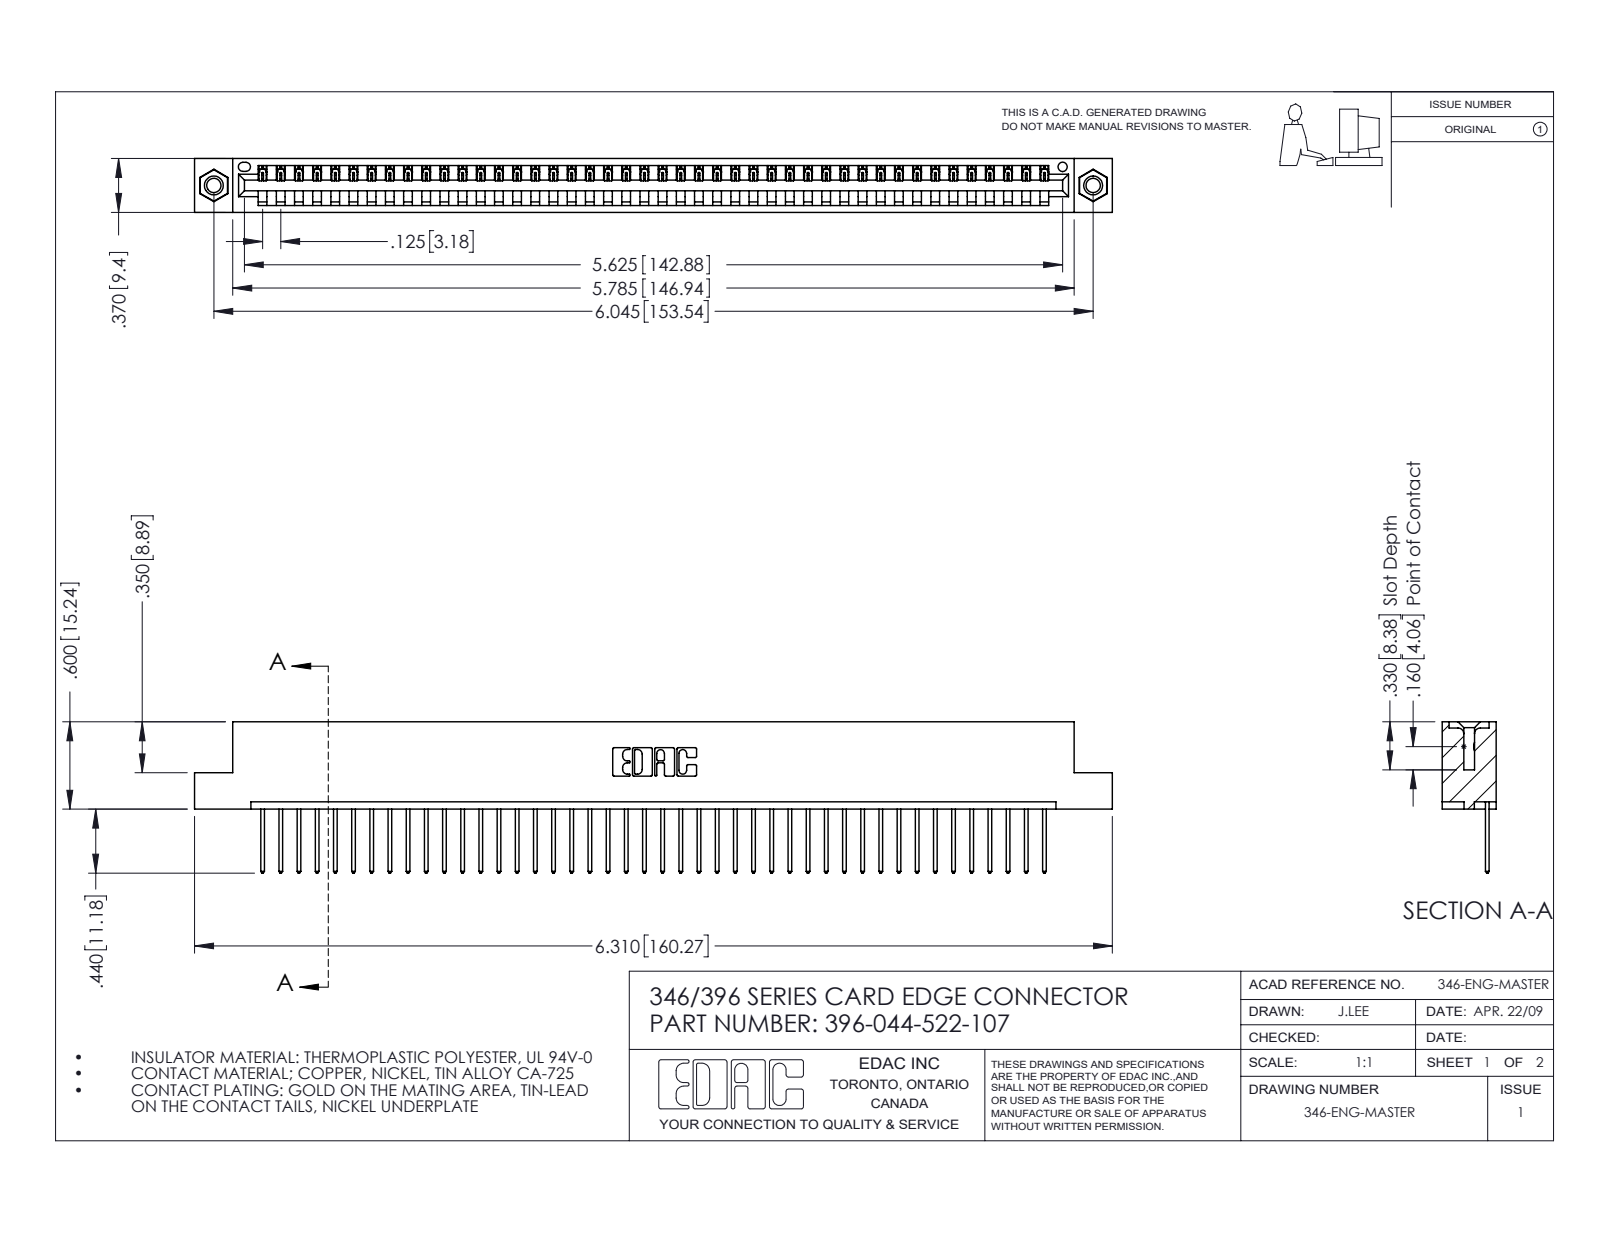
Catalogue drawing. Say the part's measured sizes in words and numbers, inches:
The part is named "345-250-001_345-250-005-103; 346 Part_Flush Mounting Lugs - 0.156 Dia-TI; 345-292-001_345-293-122; 396-044-522-107". Its 3-D file was written by "SolidWorks 2016 (CONFIG_CONTROL_DESIGN)". It is 47 solids with 2734 faces: 1868 planar, 850 cylindrical and 16 other. Overall it measures 6.31 by 1.04 by 0.37 inches. Its volume is 0.937 cubic inches and its surface area 30.07 square inches. Round holes: 2 of diameter 0.098, 2 of diameter 0.125, 2 of diameter 0.156, 1 of diameter 0.064. Round bosses or shafts: 2 of diameter 0.155. Partial cylindrical surfaces (rounded edges, fillets, slot ends): 88 of radius 0.006, 88 of radius 0.01, 22 of radius 0.01, 6 of radius 0.007, 6 of radius 0.031, 3 of radius 0.026, 2 of radius 0.031, 2 of radius 0.04. The main face-to-face distances are 0.048, 0.322, 0.37, 0.25, 0.072, 0.298, 0.025, 0.148, 0.222, 0.1. The hole center spacings are 0.246, 5.836, 6.045.
